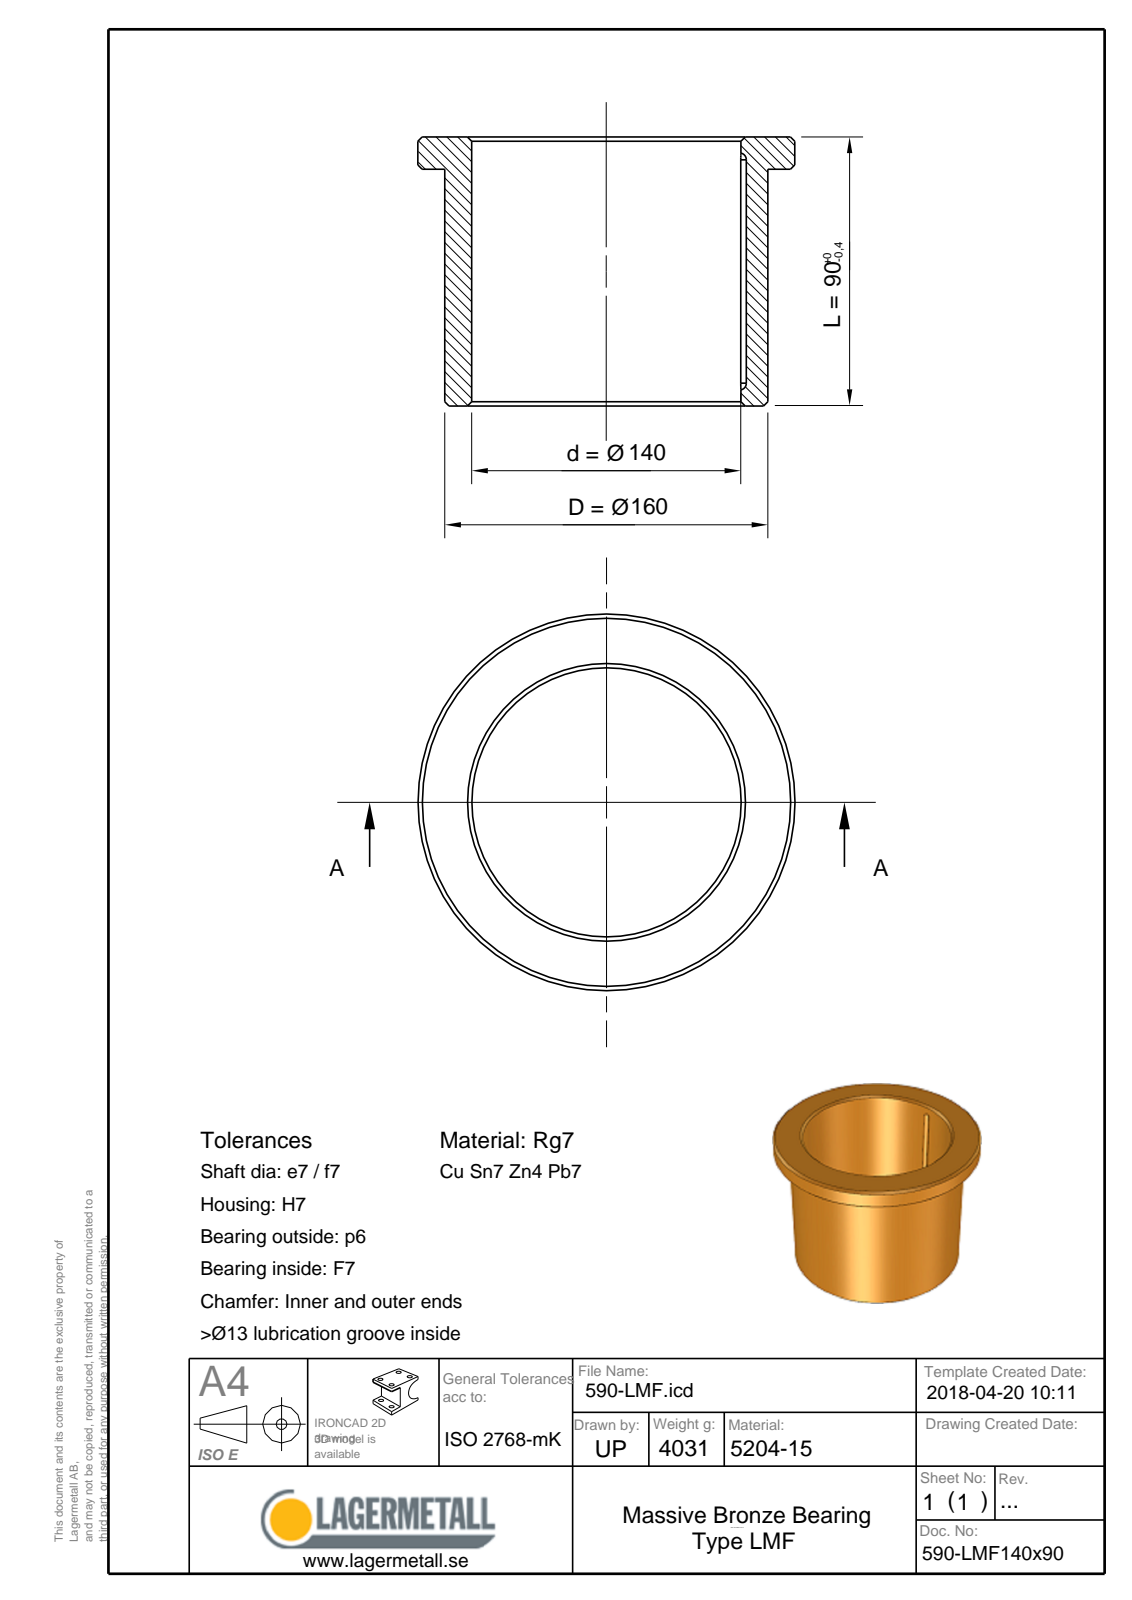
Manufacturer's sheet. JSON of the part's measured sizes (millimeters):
{"part_name": "590-LMF140x90", "step_written_by": "Spatial InterOp 3D (CONFIG_CONTROL_DESIGN)", "units": "millimeters", "bodies": {"solids": 1, "faces": 16, "planar": 4, "cylindrical": 5, "other": 7}, "overall_size": [175, 175, 90], "volume_mm3": 458083, "surface_area_mm2": 99875, "round_holes": [[140, 1]], "round_bosses_or_shafts": [[175, 1], [160, 1]], "partial_cylinders_radius": [[2.25, 2]], "face_to_face_distances": [10, 80, 90]}
